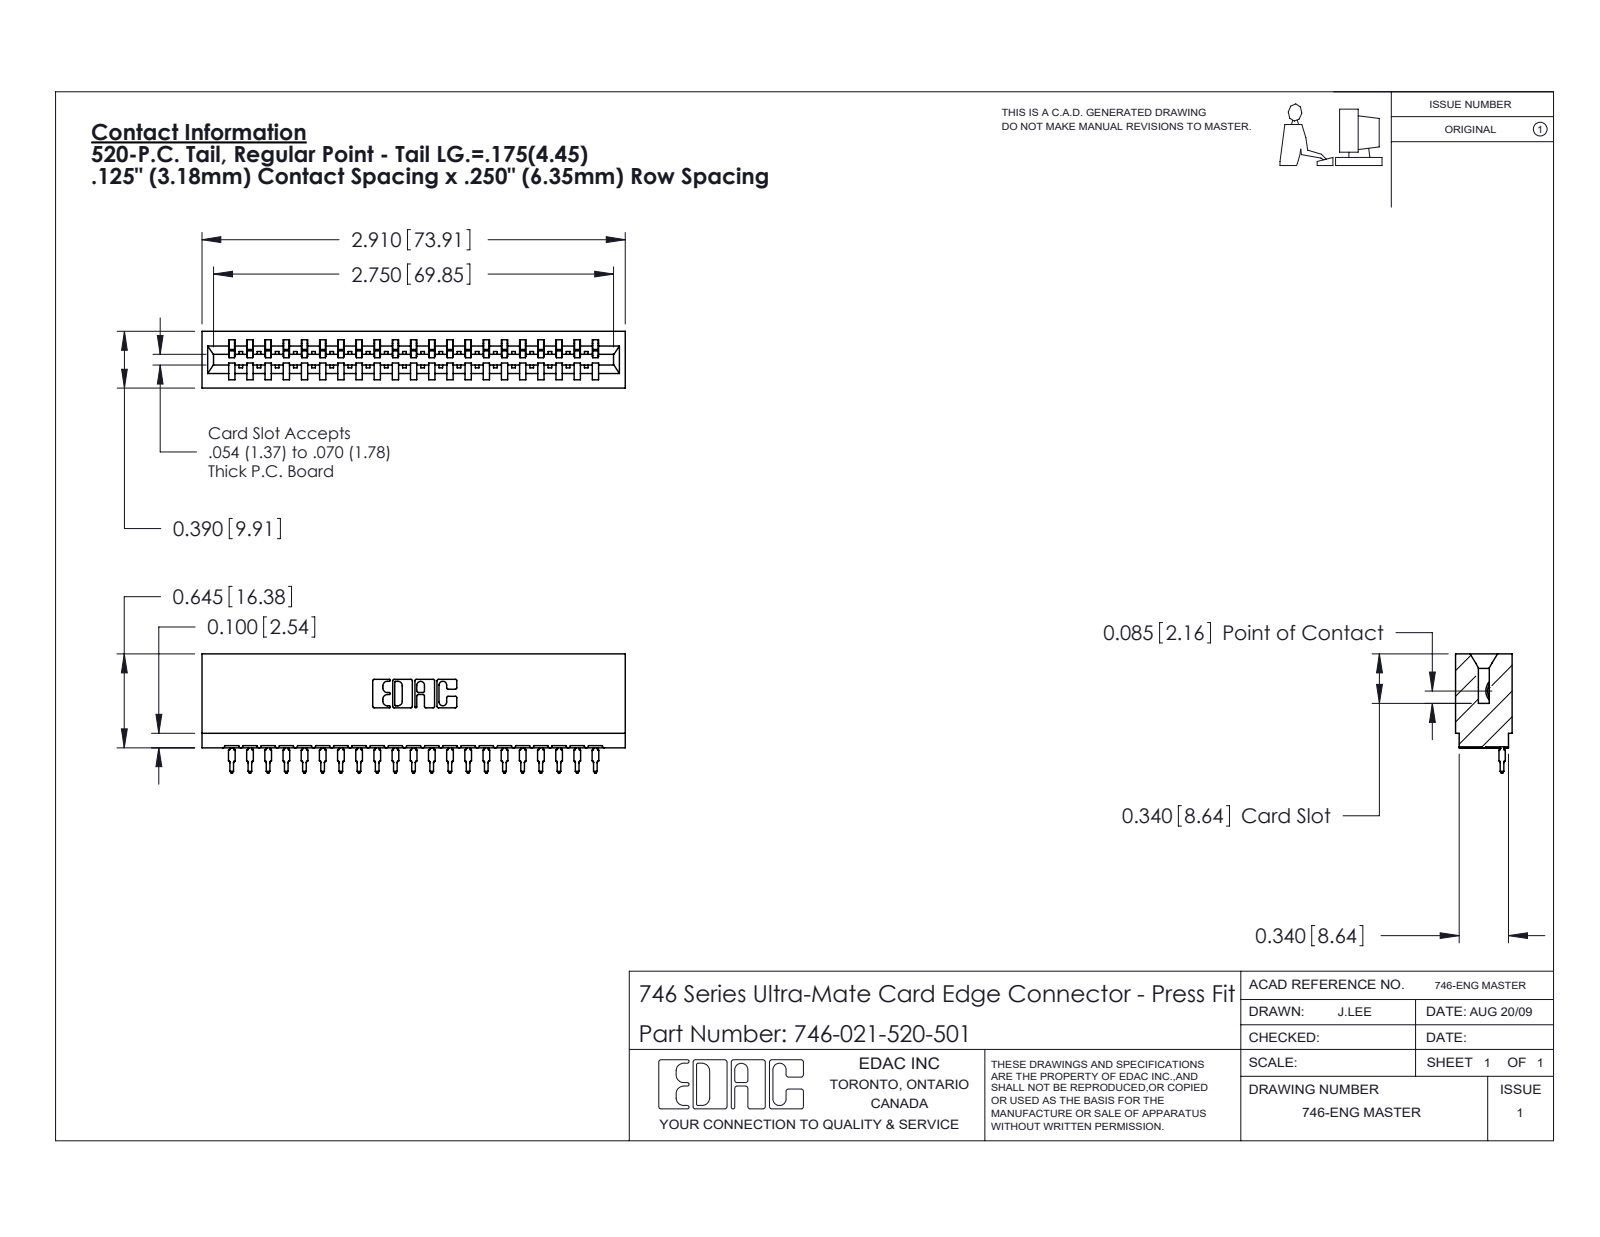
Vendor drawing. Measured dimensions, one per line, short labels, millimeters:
name: 746-292-001_520; 746-021-520-501; 746 Part_.340 Slot Depth - 01
written by: SolidWorks 2020 (CONFIG_CONTROL_DESIGN)
unit: mm
bodies: 22 solids, 2365 faces (1378 planar, 441 cylindrical, 546 other)
size: 73.9 × 20.8 × 9.9
volume: 8 390 mm³; area: 10 850 mm²
rounds: 42× R0.5, 22× R0.3, 22× R0.4, 6× R0.2, 6× R0.8, 4× R0.1, 4× R0.3, 3× R0.7
face distances: 6.4, 1.4, 8.5, 9.9, 12.7, 3.2, 7.4, 3.2, 0.6, 1.1
